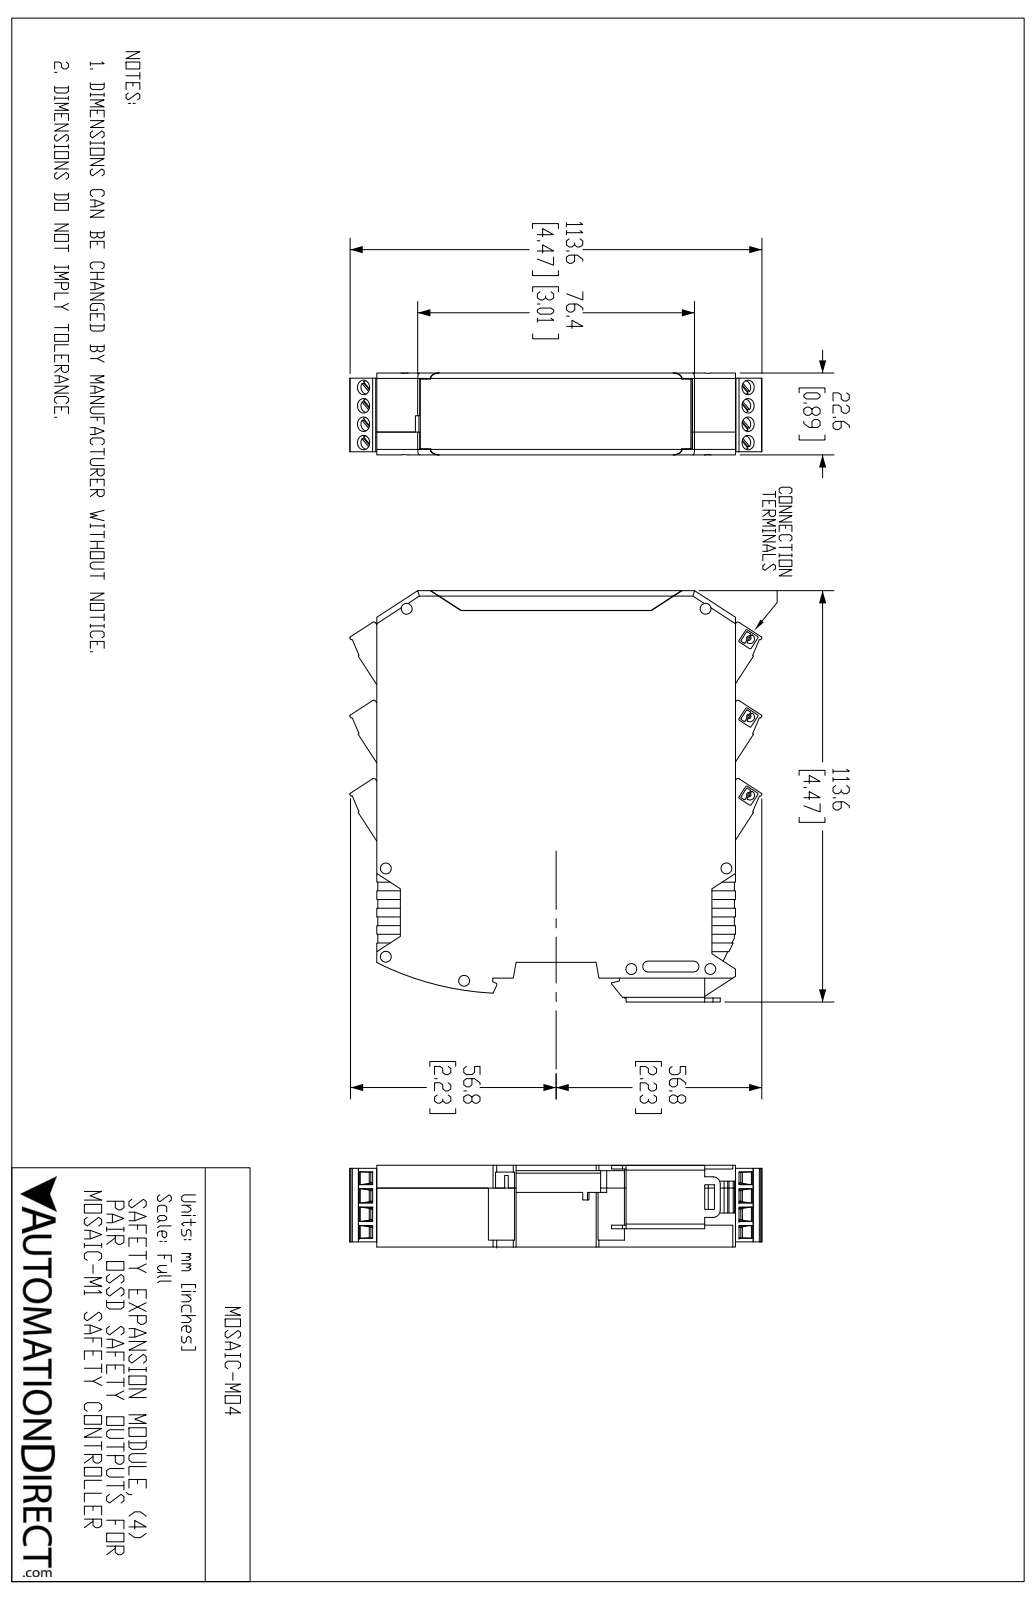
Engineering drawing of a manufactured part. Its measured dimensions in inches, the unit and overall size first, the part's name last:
Units: inches
Overall size (bounding box): 4.478 × 4.472 × 0.89
Round holes (diameter × count): ⌀0.157 ×24, ⌀0.11 ×18, ⌀0.055 ×14, ⌀0.118 ×14, ⌀0.063 ×1
Round bosses / shafts (diameter × count): ⌀0.149 ×24, ⌀0.024 ×6, ⌀0.177 ×1, ⌀0.11 ×1, ⌀0.053 ×1
Partial cylindrical surfaces — rounded edges, fillets, slot ends (radius × count): R0.008 ×60, R0.008 ×24, R0.011 ×24, R0.028 ×24, R0.115 ×24, R0.012 ×19, R0.03 ×18, R0.059 ×8
Main face-to-face distances: 0.049, 0.841, 0.89, 0.791, 0.713, 0.03, 0.039, 2.67, 0.062, 2.67
Hole centre spacings: 0.2, 0.505, 0.741, 0.4, 0.463, 0.612, 0.713, 0.948
Volume: 4.28 in³ · Surface area: 133.8 in²
Bodies: 13 solids, 2249 faces (1787 planar, 411 cylindrical, 51 other)
Part name (STEP PRODUCT): MOSAIC-MO4
STEP written by: SolidWorks 2017 (AUTOMOTIVE_DESIGN)
